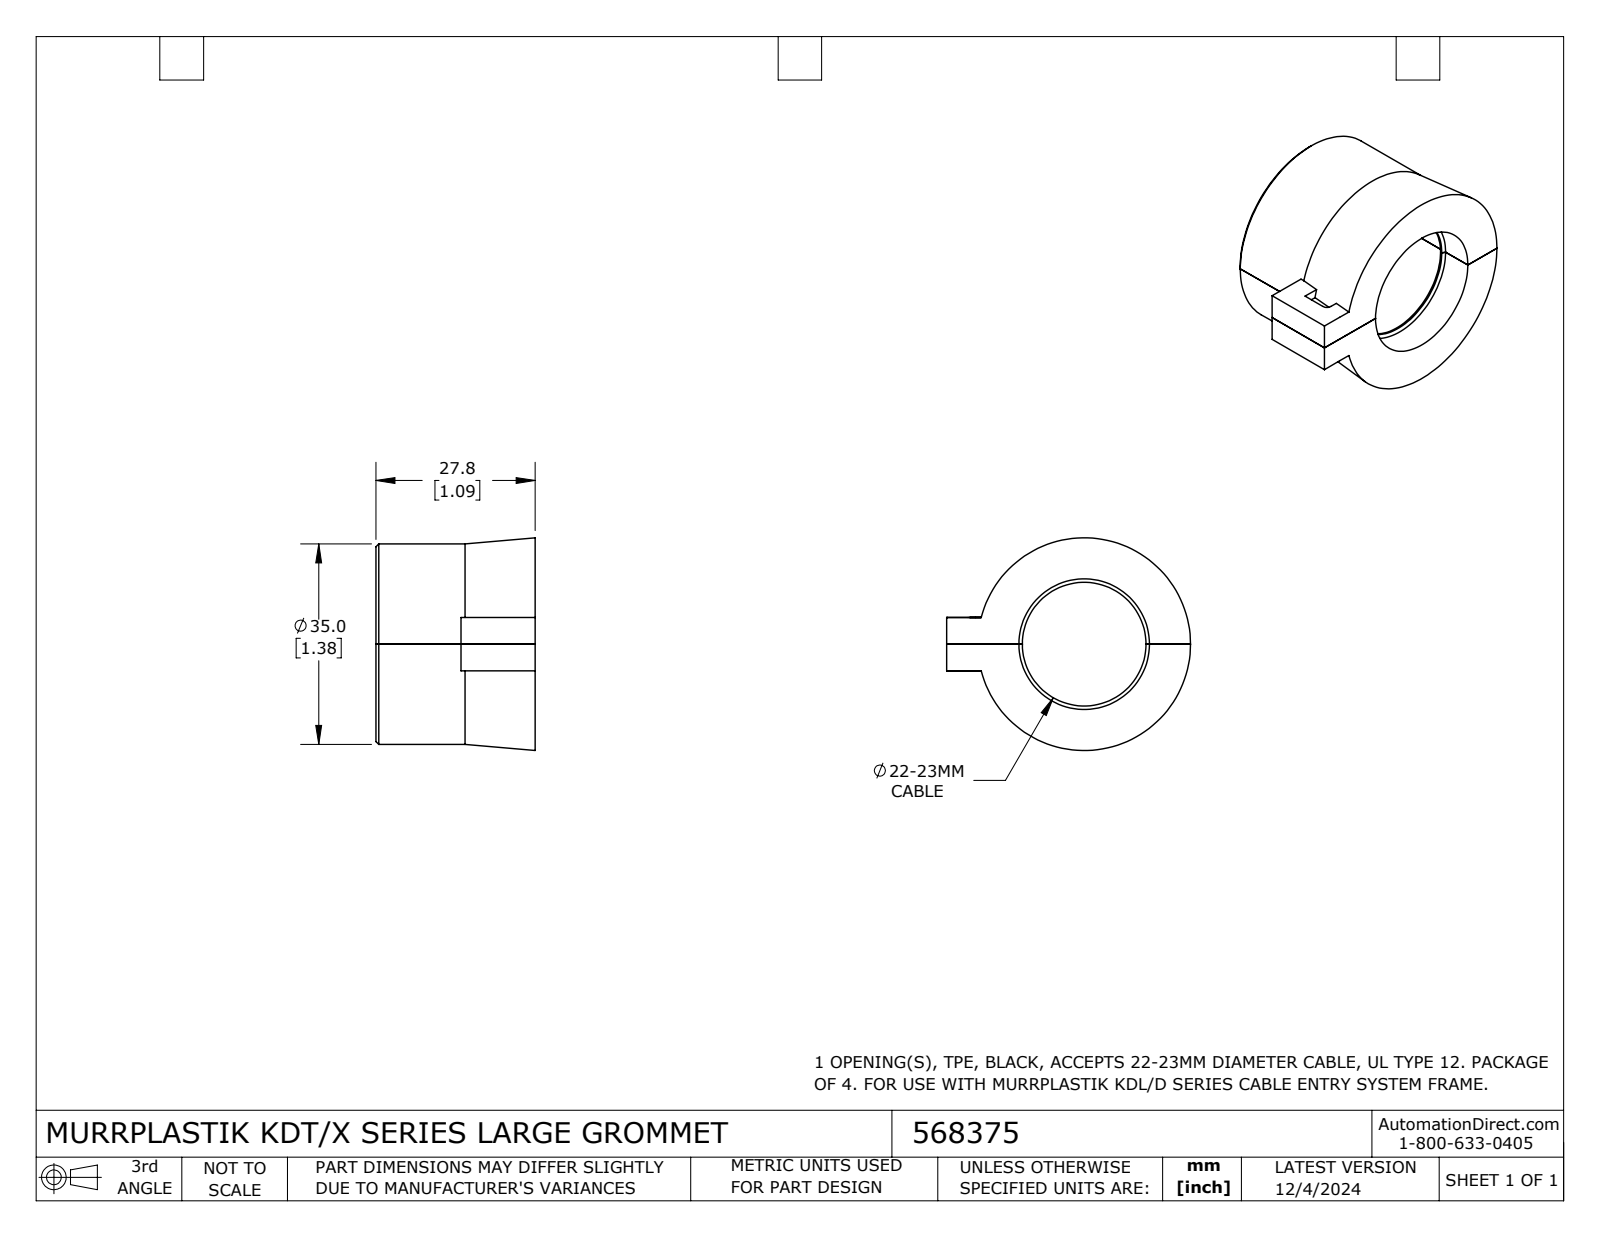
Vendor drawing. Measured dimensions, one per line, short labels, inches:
name: 568375
written by: SolidWorks 2024 (AUTOMOTIVE_DESIGN)
unit: in
bodies: 2 solids, 46 faces (22 planar, 14 cylindrical, 10 other)
size: 1.676 × 1.462 × 1.094
volume: 1.028 in³; area: 11.66 in²
holes: 1× ⌀0.85, 1× ⌀0.898
bosses: 1× ⌀1.378
rounds: 4× R0.02, 1× R0.039
face distances: 1.094, 0.183, 0.366, 0.51, 0.585, 0.061, 0.305, 0.122, 0.157, 0.243
